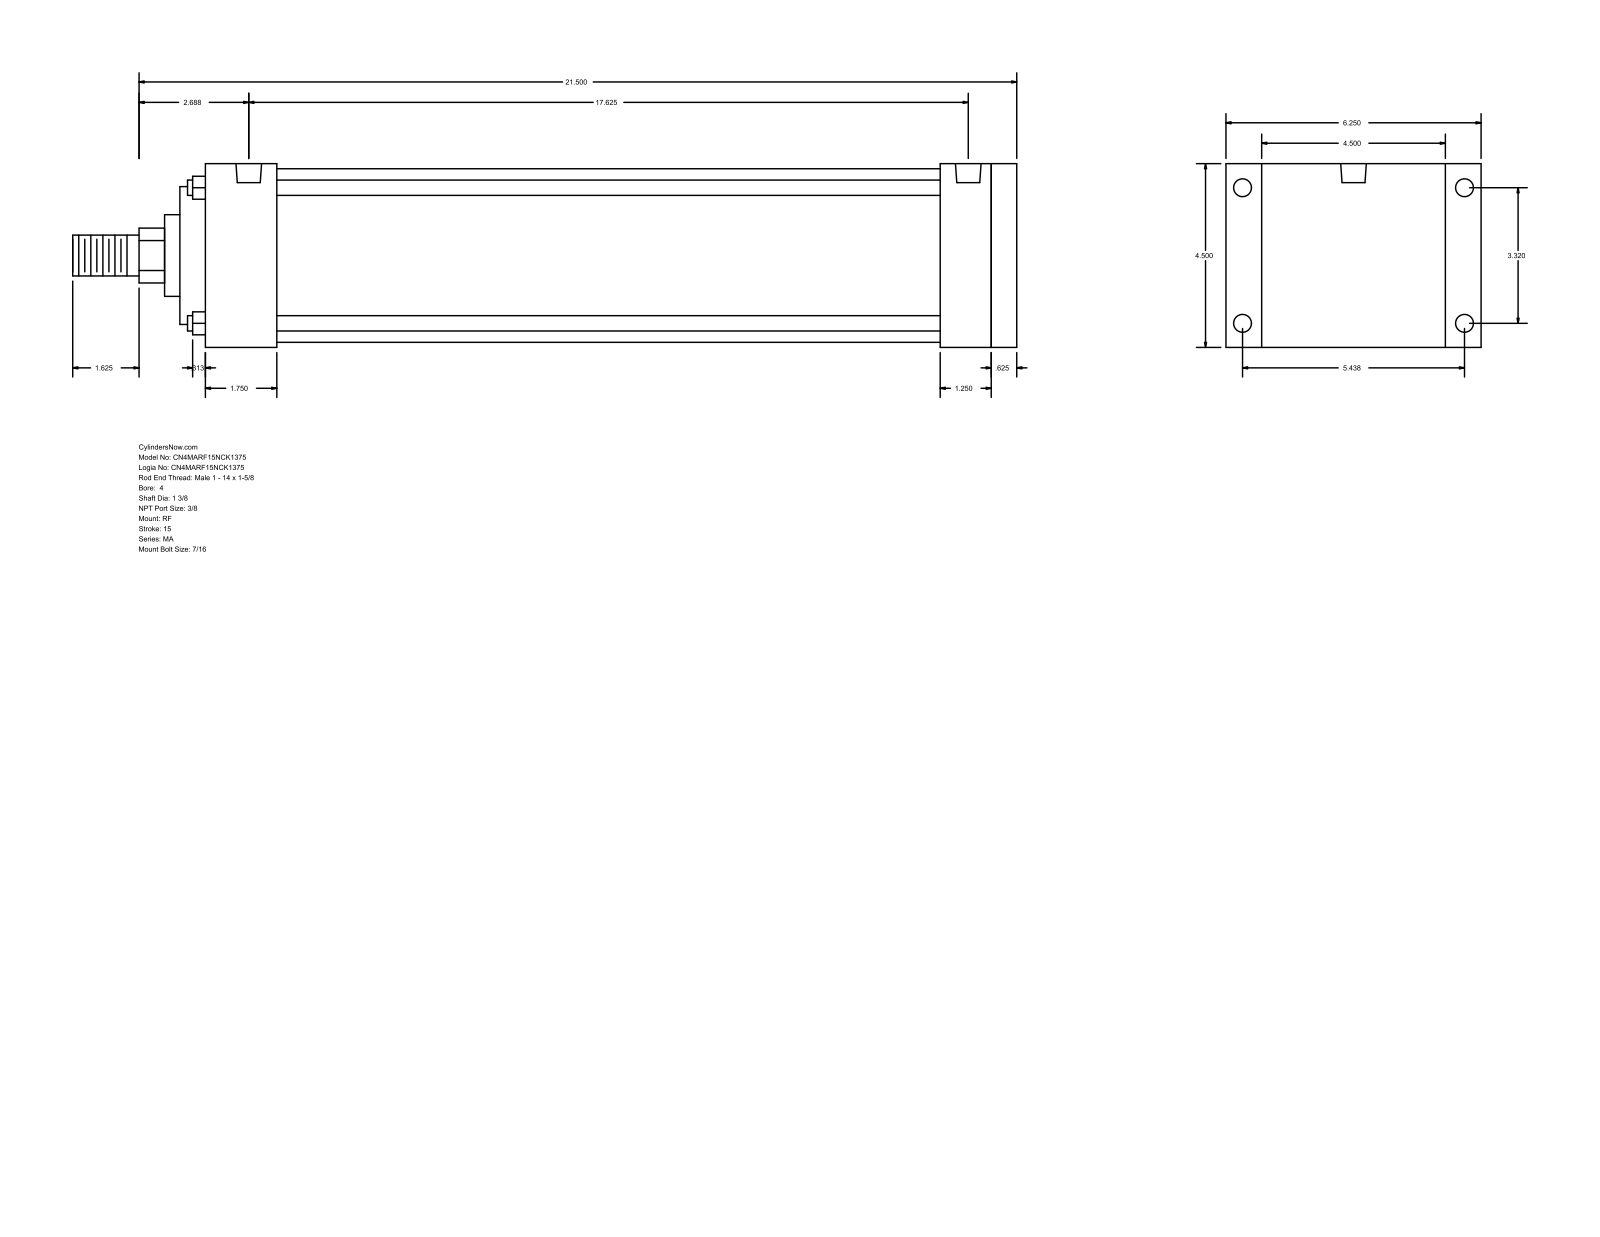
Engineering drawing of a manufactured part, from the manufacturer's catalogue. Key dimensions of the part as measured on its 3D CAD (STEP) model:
Part name (STEP PRODUCT): MA_RF__0400_1.375
STEP written by: GSSL Pune (CONFIG_CONTROL_DESIGN)
Units: millimetres
Bodies: 0 solids, 94 faces (65 planar, 29 cylindrical, 0 other)
Overall size (bounding box): 587.38 × 158.75 × 114.3
Round holes (diameter × count): ⌀11.11 ×8, ⌀15.93 ×2
Round bosses / shafts (diameter × count): ⌀9.53 ×4, ⌀107.95 ×1, ⌀85.72 ×1, ⌀50.8 ×1, ⌀34.92 ×1, ⌀25.4 ×1
Partial cylindrical surfaces — rounded edges, fillets, slot ends (radius × count): R17.06 ×1
Main face-to-face distances: 114.3, 504.83, 15.87, 488.96, 520.7, 22.23, 136.53, 473.08, 457.21, 31.75
Hole centre spacings: 84.32, 138.12, 161.82, 438.15, 4.76, 4.77, 442.91, 442.92
